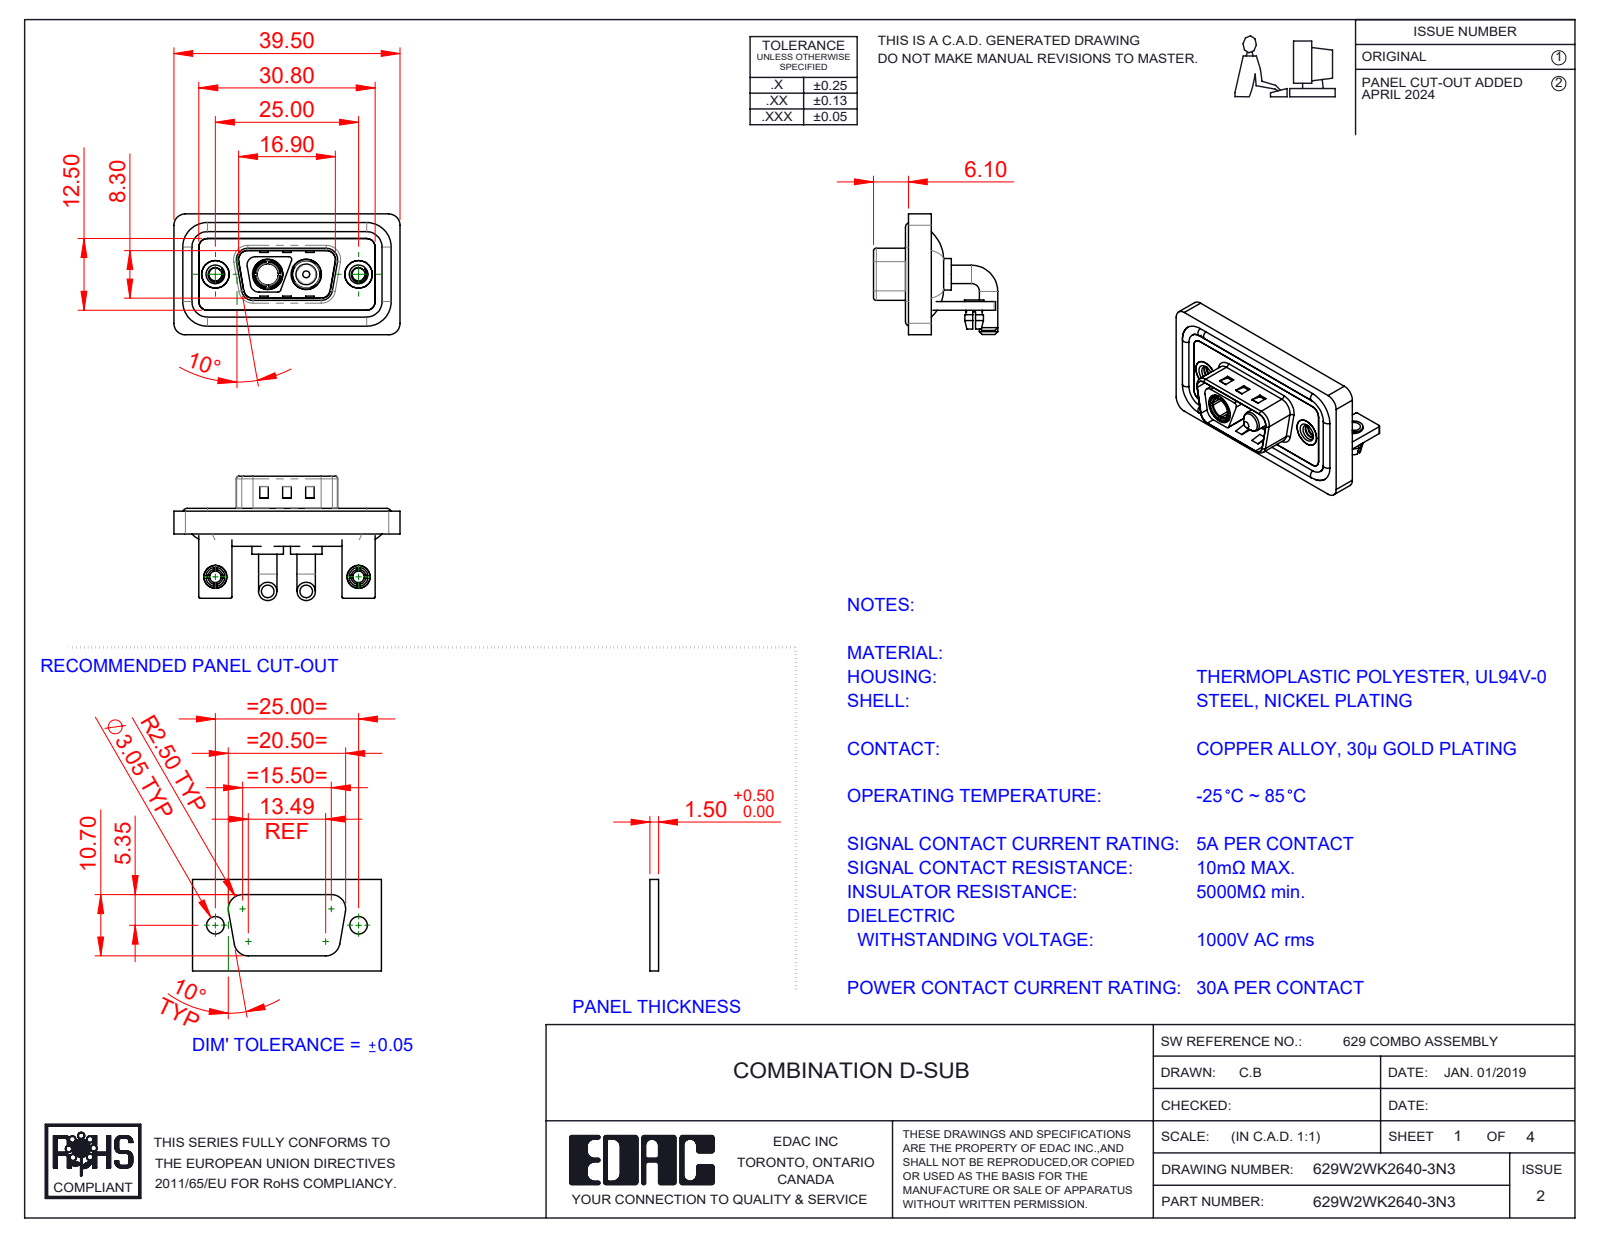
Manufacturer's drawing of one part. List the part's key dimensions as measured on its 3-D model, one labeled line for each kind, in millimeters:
Part name (STEP PRODUCT): Power Pin_30A RA; 629Combo Shell Front_09 Contacts; 629Combo Threaded Rivet_3; 629Combo Housing_2WK2 (+6 more)
STEP written by: SolidWorks 2023 (CONFIG_CONTROL_DESIGN)
Units: millimetres
Bodies: 15 solids, 674 faces (257 planar, 281 cylindrical, 136 other)
Overall size (bounding box): 39.5 × 21.7 × 21.1
Volume: 5 054 mm³ · Surface area: 8 367 mm²
Round holes (diameter × count): ⌀2 ×2, ⌀2.26 ×2, ⌀2.5 ×2, ⌀3.2 ×2, ⌀4 ×2, ⌀4.8 ×2, ⌀4.85 ×2, ⌀5 ×2, ⌀5.3 ×2, ⌀3.7 ×1
Round bosses / shafts (diameter × count): ⌀3.2 ×4, ⌀1.6 ×4, ⌀5.5 ×2, ⌀5.2 ×2, ⌀4.9 ×2, ⌀4.75 ×2, ⌀4 ×2, ⌀3.75 ×2
Partial cylindrical surfaces — rounded edges, fillets, slot ends (radius × count): R1.5 ×20, R2 ×19, R0.25 ×16, R0.5 ×11, R1.6 ×8, R0.6 ×4, R0.65 ×4, R0.9 ×4
Main face-to-face distances: 0.4, 1.5, 2.9, 0.8, 1.1, 1.2, 2.1, 1.6, 3.7, 2.5
Hole centre spacings: 9.14, 15.86, 25, 6.72
